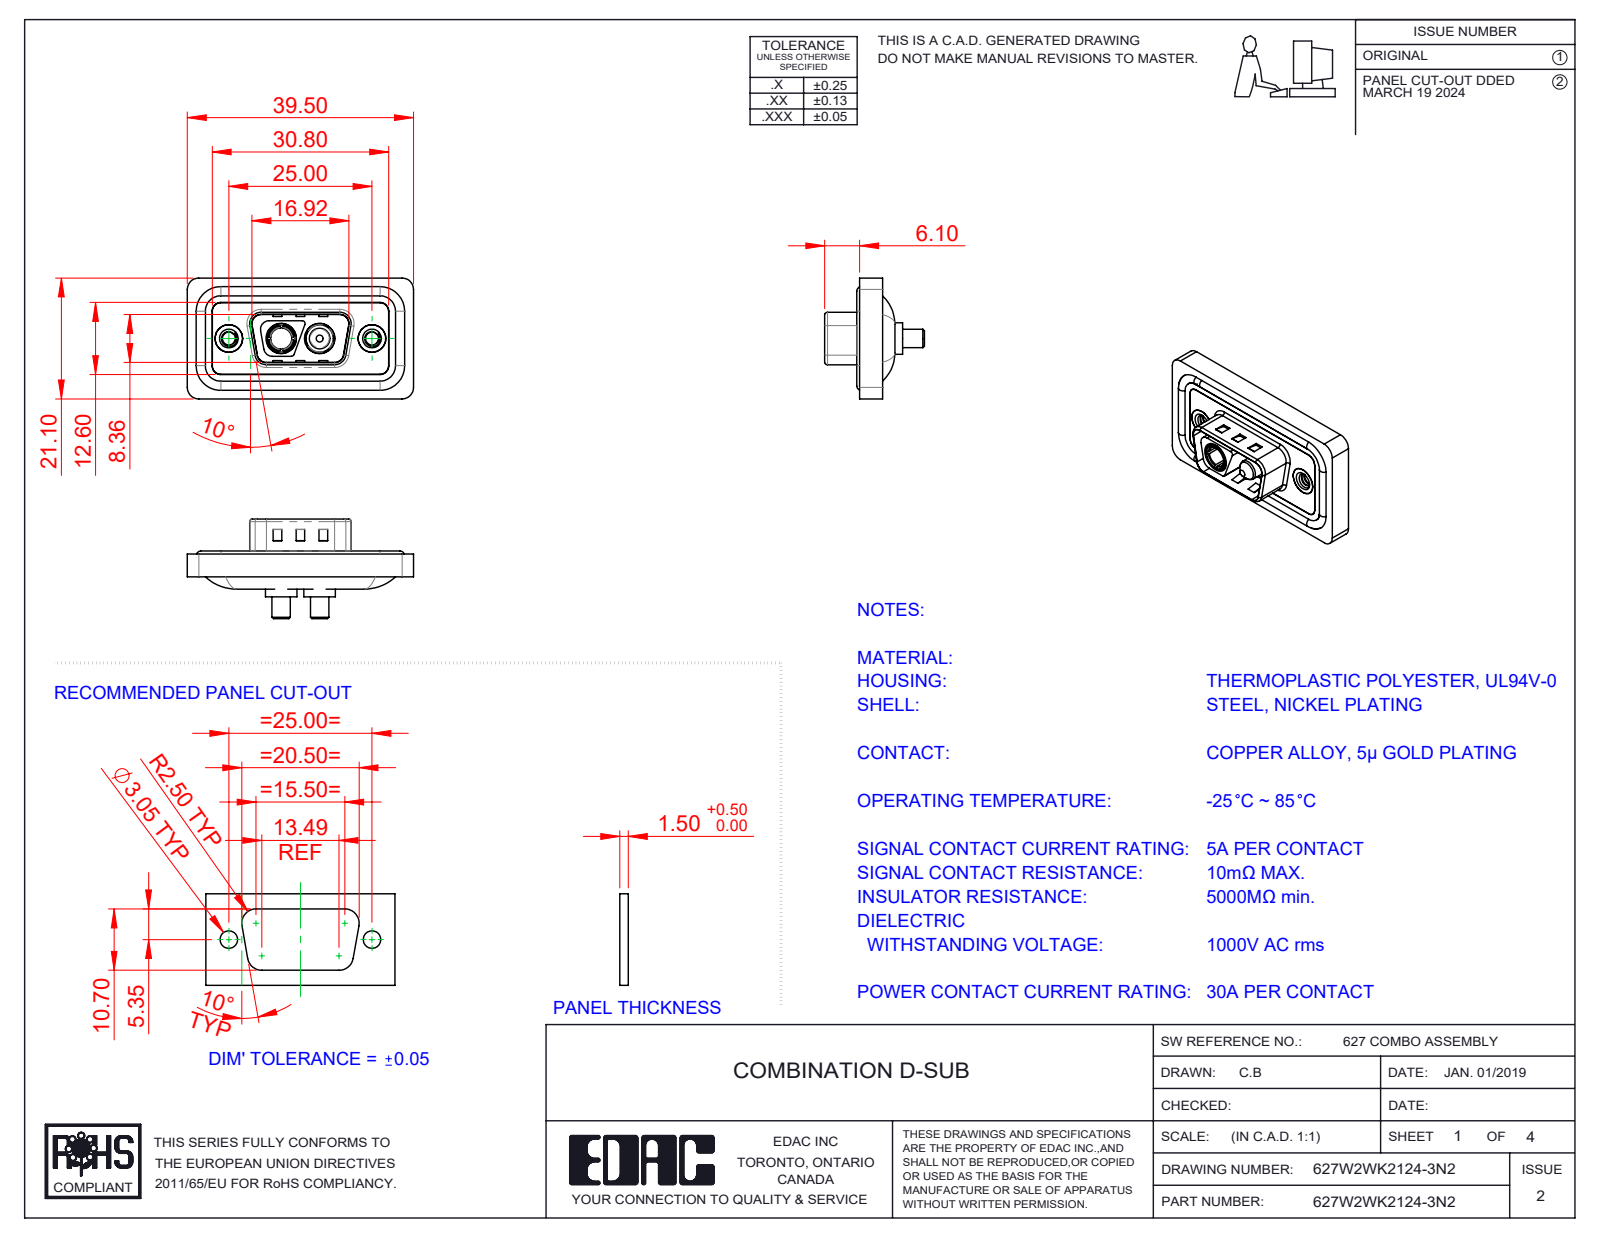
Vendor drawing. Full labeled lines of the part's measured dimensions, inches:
Part name (STEP PRODUCT): 627W2WK2124-3N2; 627Combo Housing_2WK2; 627Combo Shell Front_09 Contacts; Power Pin_30A S (+4 more)
STEP written by: SolidWorks 2023 (CONFIG_CONTROL_DESIGN)
Units: inches
Bodies: 11 solids, 534 faces (189 planar, 227 cylindrical, 118 other)
Overall size (bounding box): 1.555 × 0.831 × 0.685
Volume: 0.279 in³ · Surface area: 11.39 in²
Round holes (diameter × count): ⌀0.089 ×2, ⌀0.157 ×2, ⌀0.189 ×2, ⌀0.191 ×2, ⌀0.197 ×2, ⌀0.209 ×2, ⌀0.146 ×1
Round bosses / shafts (diameter × count): ⌀0.063 ×4, ⌀0.217 ×2, ⌀0.205 ×2, ⌀0.193 ×2, ⌀0.187 ×2, ⌀0.148 ×2, ⌀0.126 ×2, ⌀0.195 ×1
Partial cylindrical surfaces — rounded edges, fillets, slot ends (radius × count): R0.059 ×24, R0.079 ×18, R0.02 ×10, R0.063 ×8, R0.01 ×4, R0.024 ×4, R0.026 ×4, R0.035 ×4
Main face-to-face distances: 0.016, 0.043, 0.114, 0.02, 0.122, 0.063, 0.059, 0.157, 0.098, 0.071
Hole centre spacings: 0.36, 0.624, 0.265, 0.984
